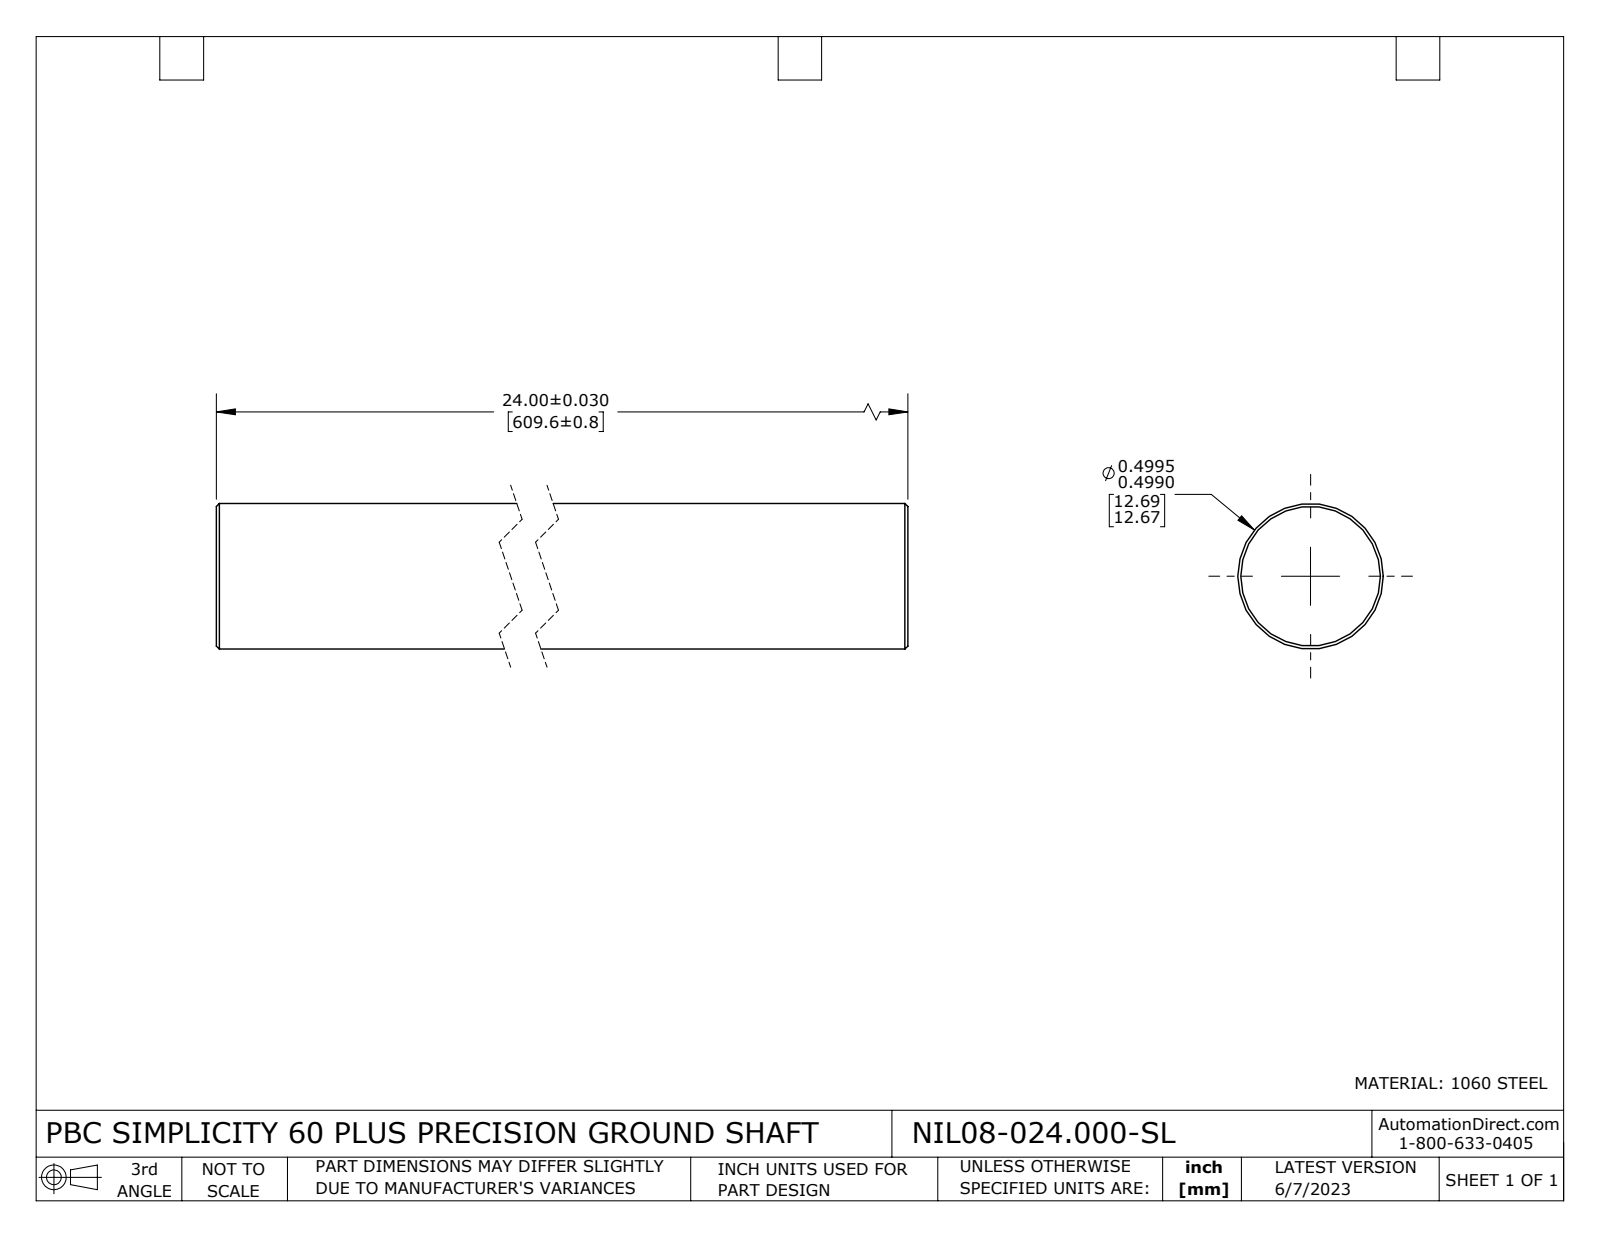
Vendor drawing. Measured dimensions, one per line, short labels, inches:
name: NIL08-024.000-SL
written by: SolidWorks 2021 (CONFIG_CONTROL_DESIGN)
unit: in
bodies: 1 solid, 8 faces (2 planar, 2 cylindrical, 4 other)
size: 24 × 0.5 × 0.5
volume: 4.712 in³; area: 38.07 in²
bosses: 1× ⌀0.5
face distances: 24
